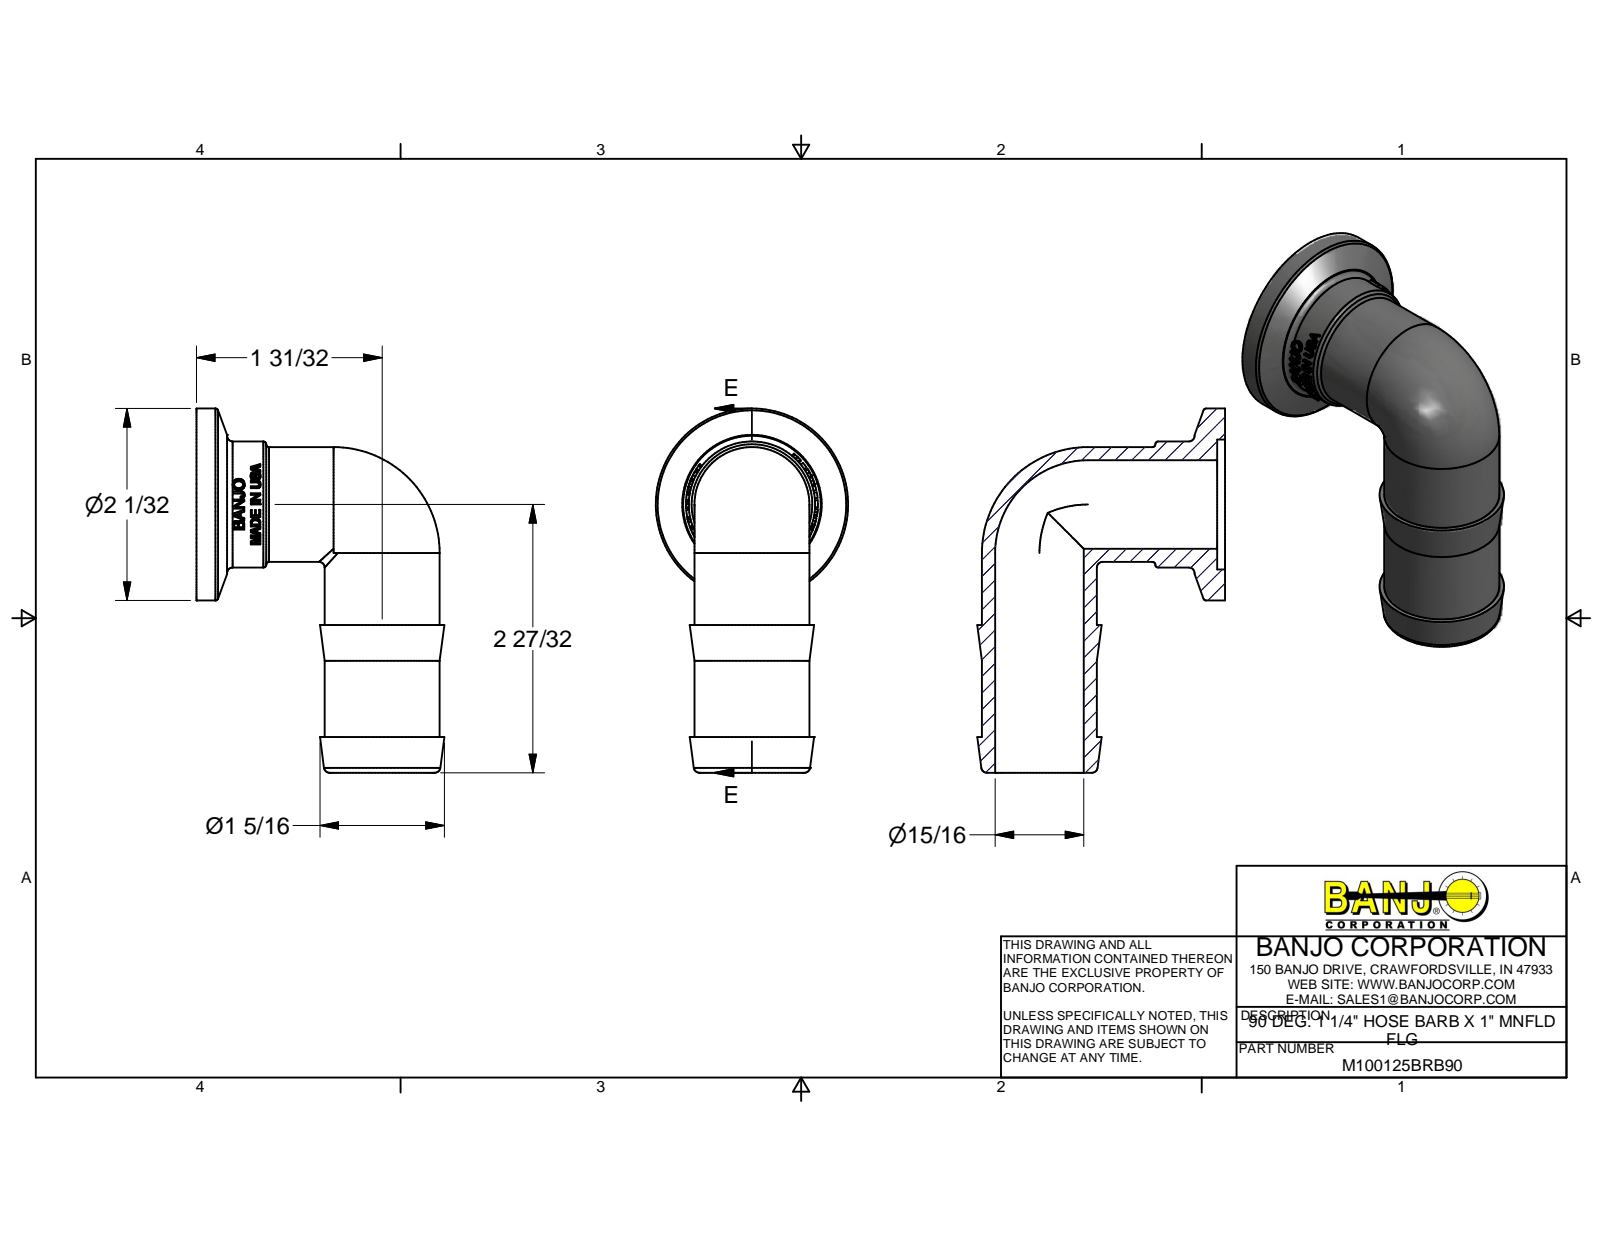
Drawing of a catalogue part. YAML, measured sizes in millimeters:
part_name: "M100125BRB90U; M100125BRB90"
step_written_by: "Autodesk Inventor 2014 (AUTOMOTIVE_DESIGN)"
units: millimeters
bodies: {solids: 1, faces: 442, planar: 170, cylindrical: 51, other: 221}
overall_size: [98.3, 66.8, 51.82]
volume: 47547
surface_area: 24258
round_holes:
  - {diameter: 23.88, count: 2}
  - {diameter: 35.05, count: 1}
round_bosses_or_shafts:
  - {diameter: 30.99, count: 2}
  - {diameter: 51.82, count: 1}
  - {diameter: 34.04, count: 1}
partial_cylinders:
  - {radius: 17.78, count: 1}
face_to_face_distances: [2.13, 9.66, 39.88, 30.22, 6.1, 8.23, 6.54, 12.64, 14.77, 3.05]
